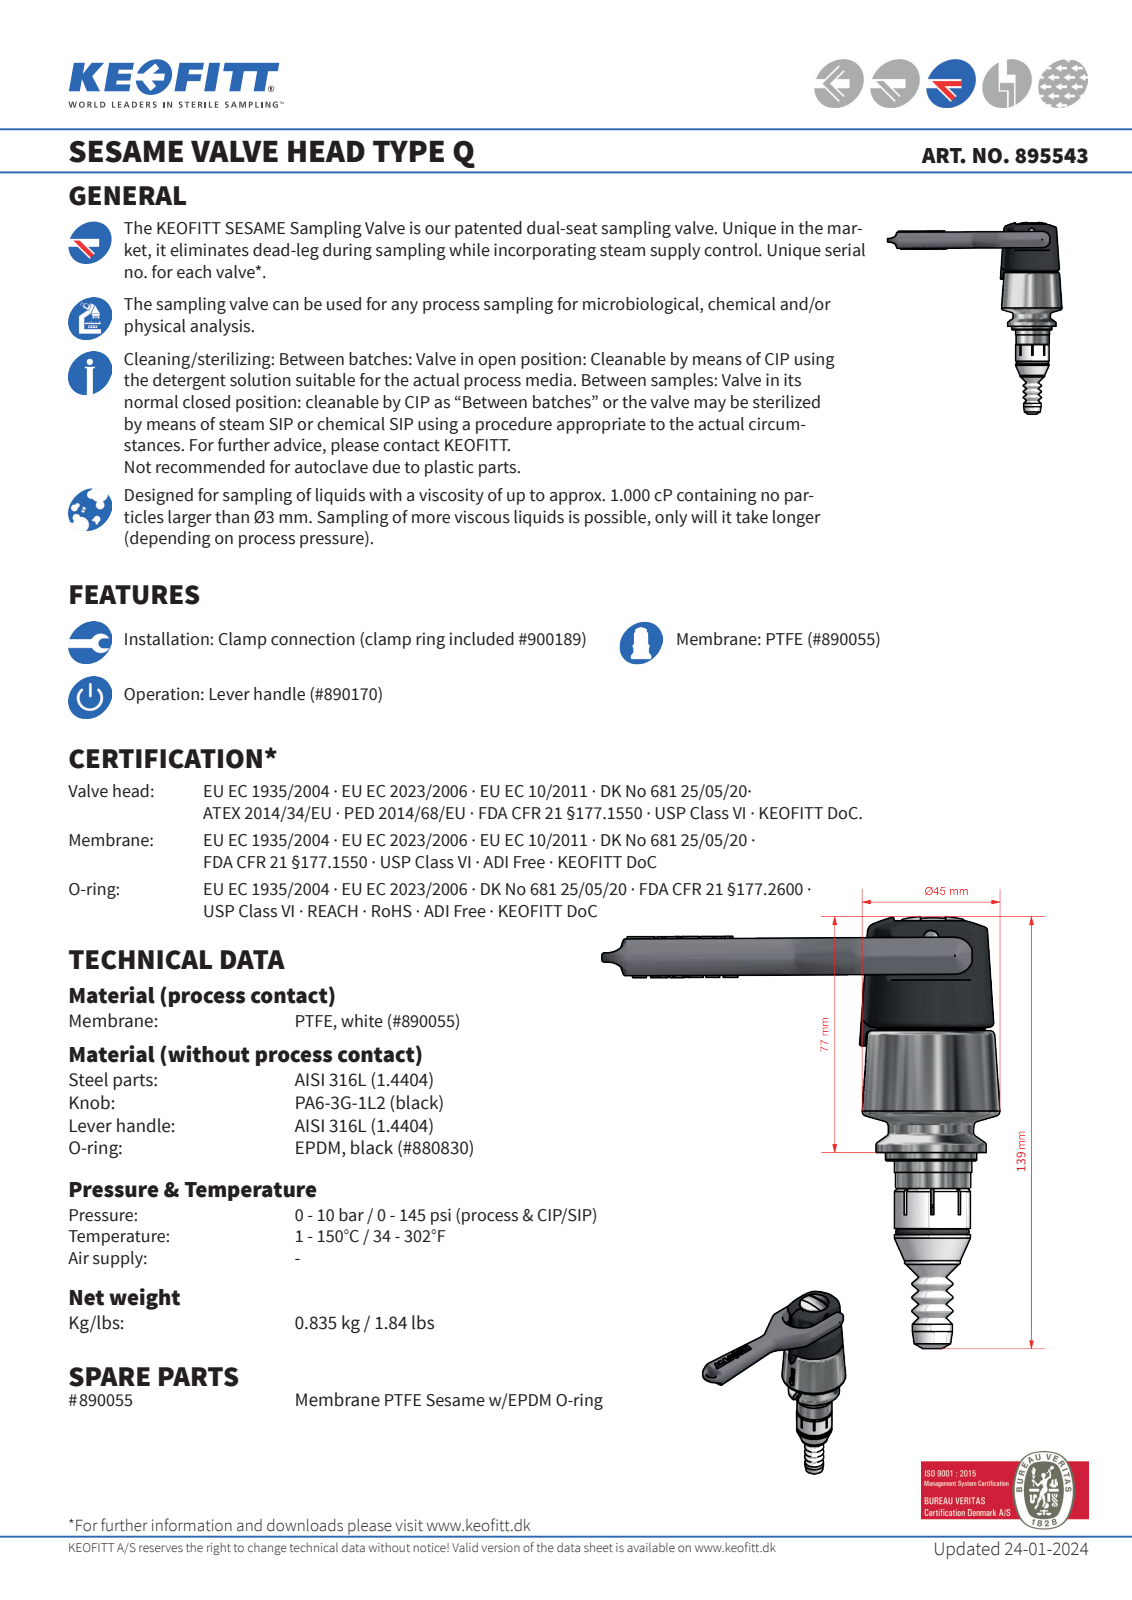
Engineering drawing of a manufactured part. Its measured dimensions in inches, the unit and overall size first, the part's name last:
Units: inches
Overall size (bounding box): 5.683 × 5.61 × 1.836
Round holes (diameter × count): ⌀0.709 ×1
Round bosses / shafts (diameter × count): ⌀1.759 ×1, ⌀1.378 ×1, ⌀1.177 ×1, ⌀1.102 ×1, ⌀0.992 ×1, ⌀0.976 ×1, ⌀0.965 ×1, ⌀0.803 ×1
Partial cylindrical surfaces — rounded edges, fillets, slot ends (radius × count): R0.004 ×74, R0.039 ×46, R0.02 ×38, R0.098 ×16, R0.059 ×5, R0.079 ×2, R0.085 ×2, R0.197 ×2
Main face-to-face distances: 0.472, 0.315, 0.016, 1.039, 2.624, 0.157, 2.467, 3.096, 2.781, 2.309
Volume: 8.074 in³ · Surface area: 54.98 in²
Bodies: 2 solids, 1013 faces (304 planar, 310 cylindrical, 399 other)
Part name (STEP PRODUCT): 895543
STEP written by: Autodesk Inventor 2022 (AUTOMOTIVE_DESIGN)
